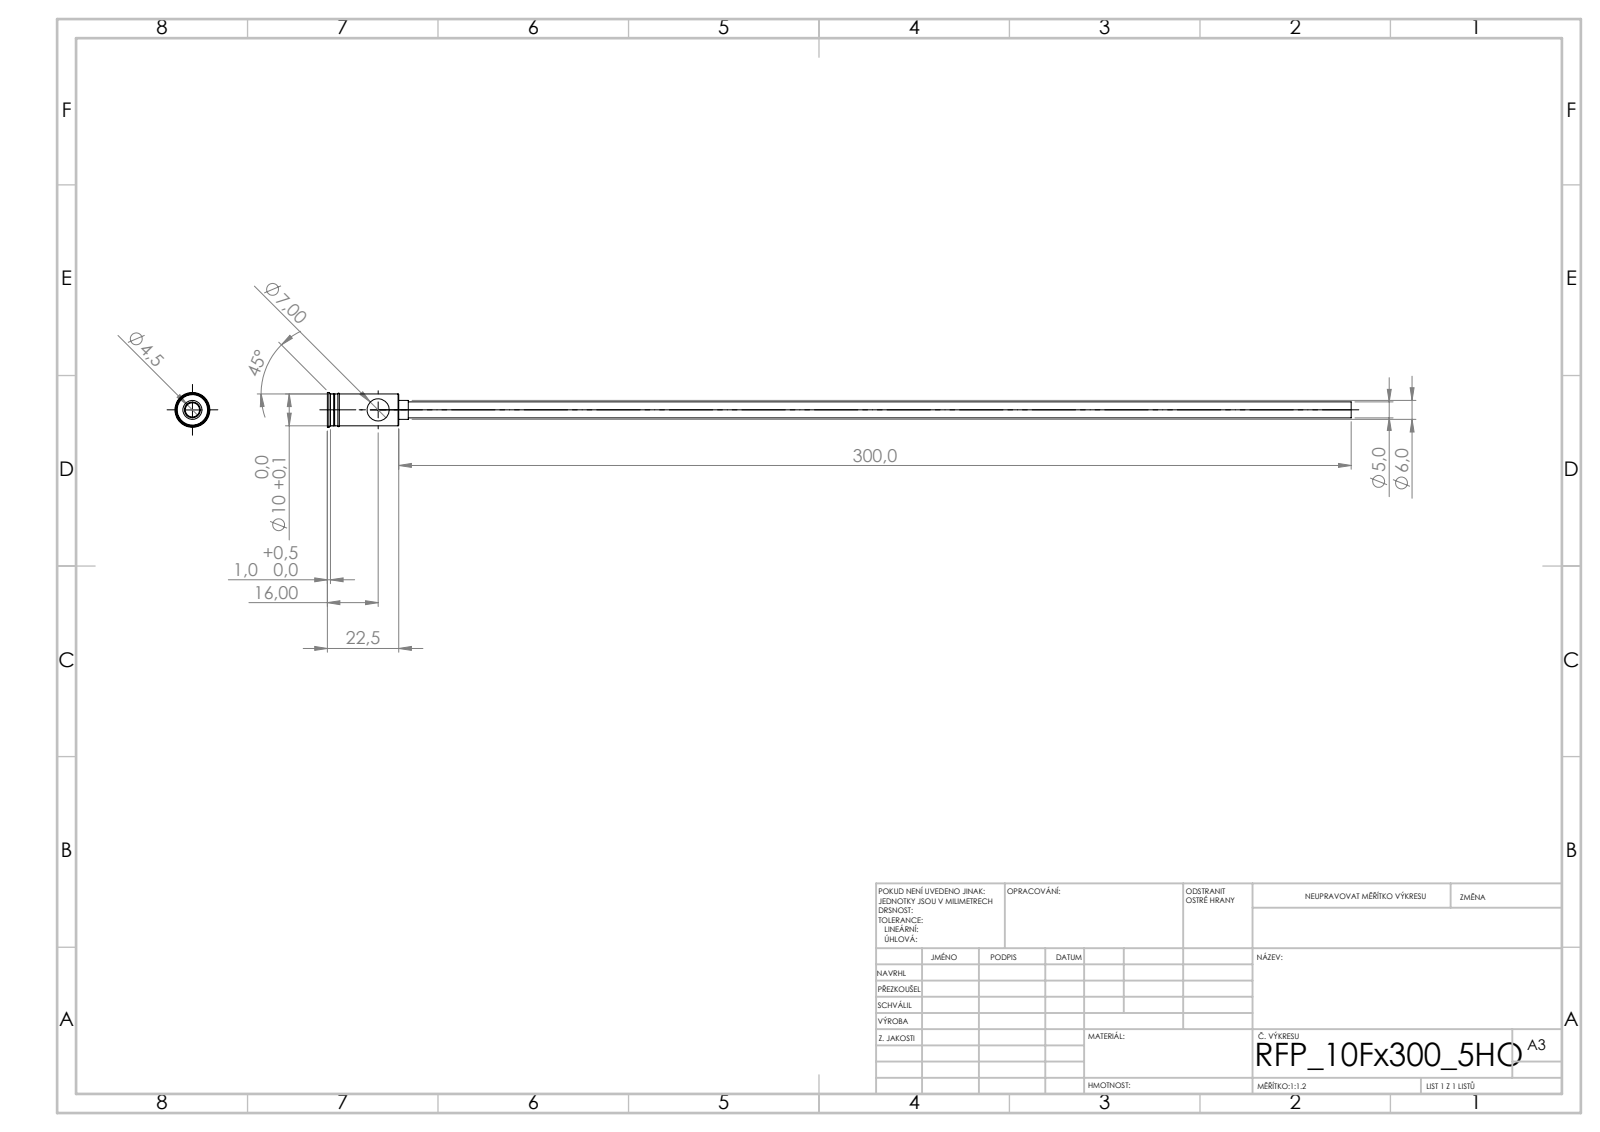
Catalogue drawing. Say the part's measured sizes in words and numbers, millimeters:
Its 3-D file was written by "SolidWorks 2019 (CONFIG_CONTROL_DESIGN)". It is 1 solid with 44 faces: 20 planar, 16 cylindrical and 8 other. Overall it measures 322.5 by 11 by 11 millimeters. Its volume is 2 465 cubic millimeters and its surface area 10 032 square millimeters. Round holes: 1 of diameter 4.5, 1 of diameter 7. Round bosses or shafts: 1 of diameter 11, 1 of diameter 10, 1 of diameter 6, 1 of diameter 5. The main face-to-face distances are 22.5, 20.5, 2, 5.4, 20.2, 2.3, 3, 23.2, 23.5, 25.5.
